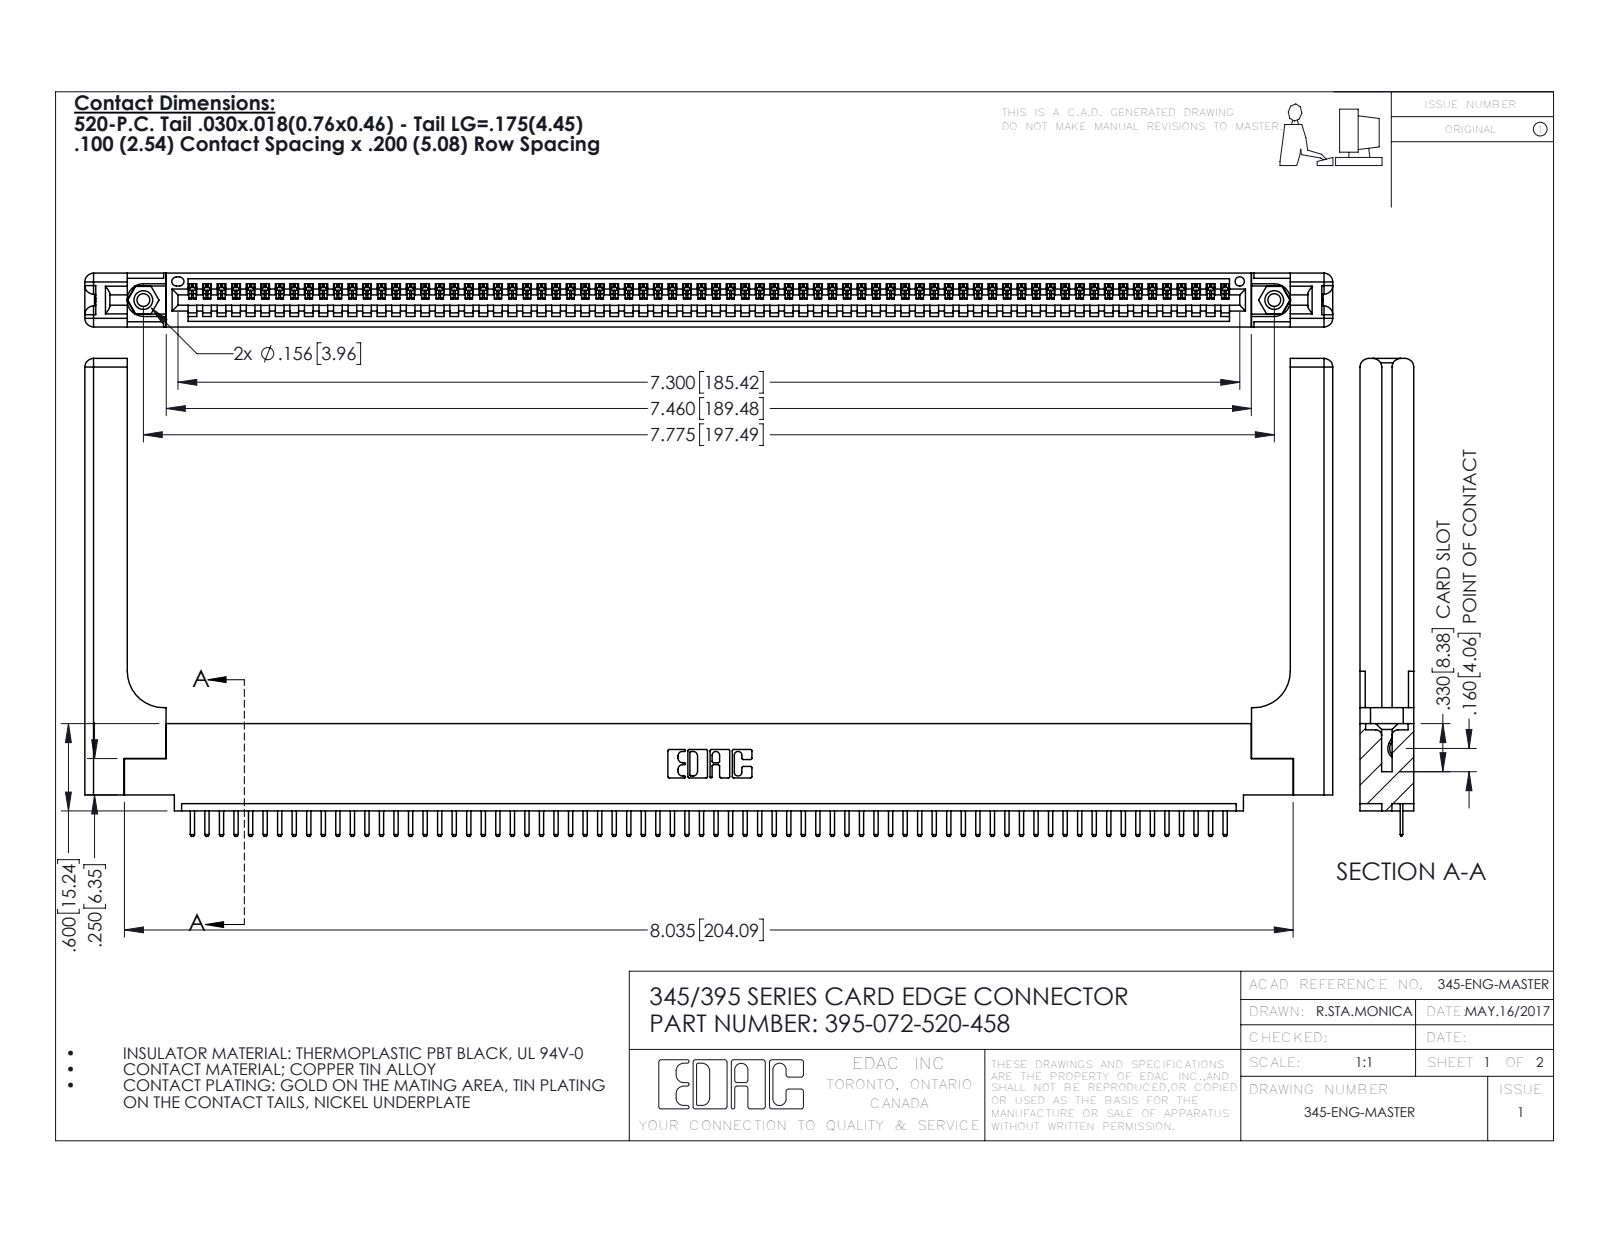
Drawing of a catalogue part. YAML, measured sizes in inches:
part_name: "345-292-001_345-293-120; 345-220-058_345-220-058; 345 Part_0.110 Offset - 0.156 Dia-TH; 395-072-520-458 (+1 more)"
step_written_by: "SolidWorks 2016 (CONFIG_CONTROL_DESIGN)"
units: inches
bodies: {solids: 77, faces: 4850, planar: 3256, cylindrical: 1534, other: 60}
overall_size: [8.579, 3.285, 0.37]
volume: 1.78
surface_area: 50.49
round_holes:
  - {diameter: 0.089, count: 2}
  - {diameter: 0.125, count: 2}
  - {diameter: 0.156, count: 2}
  - {diameter: 0.064, count: 1}
round_bosses_or_shafts:
  - {diameter: 0.155, count: 2}
partial_cylinders:
  - {radius: 0.01, count: 146}
  - {radius: 0.006, count: 144}
  - {radius: 0.01, count: 22}
  - {radius: 0.06, count: 16}
  - {radius: 0.007, count: 6}
  - {radius: 0.031, count: 6}
  - {radius: 0.026, count: 3}
  - {radius: 0.03, count: 2}
face_to_face_distances: [0.072, 0.37, 0.298, 0.098, 0.272, 0.025, 0.2, 0.225, 0.148, 0.15]
hole_center_spacings: [0.27, 7.539, 7.775]
